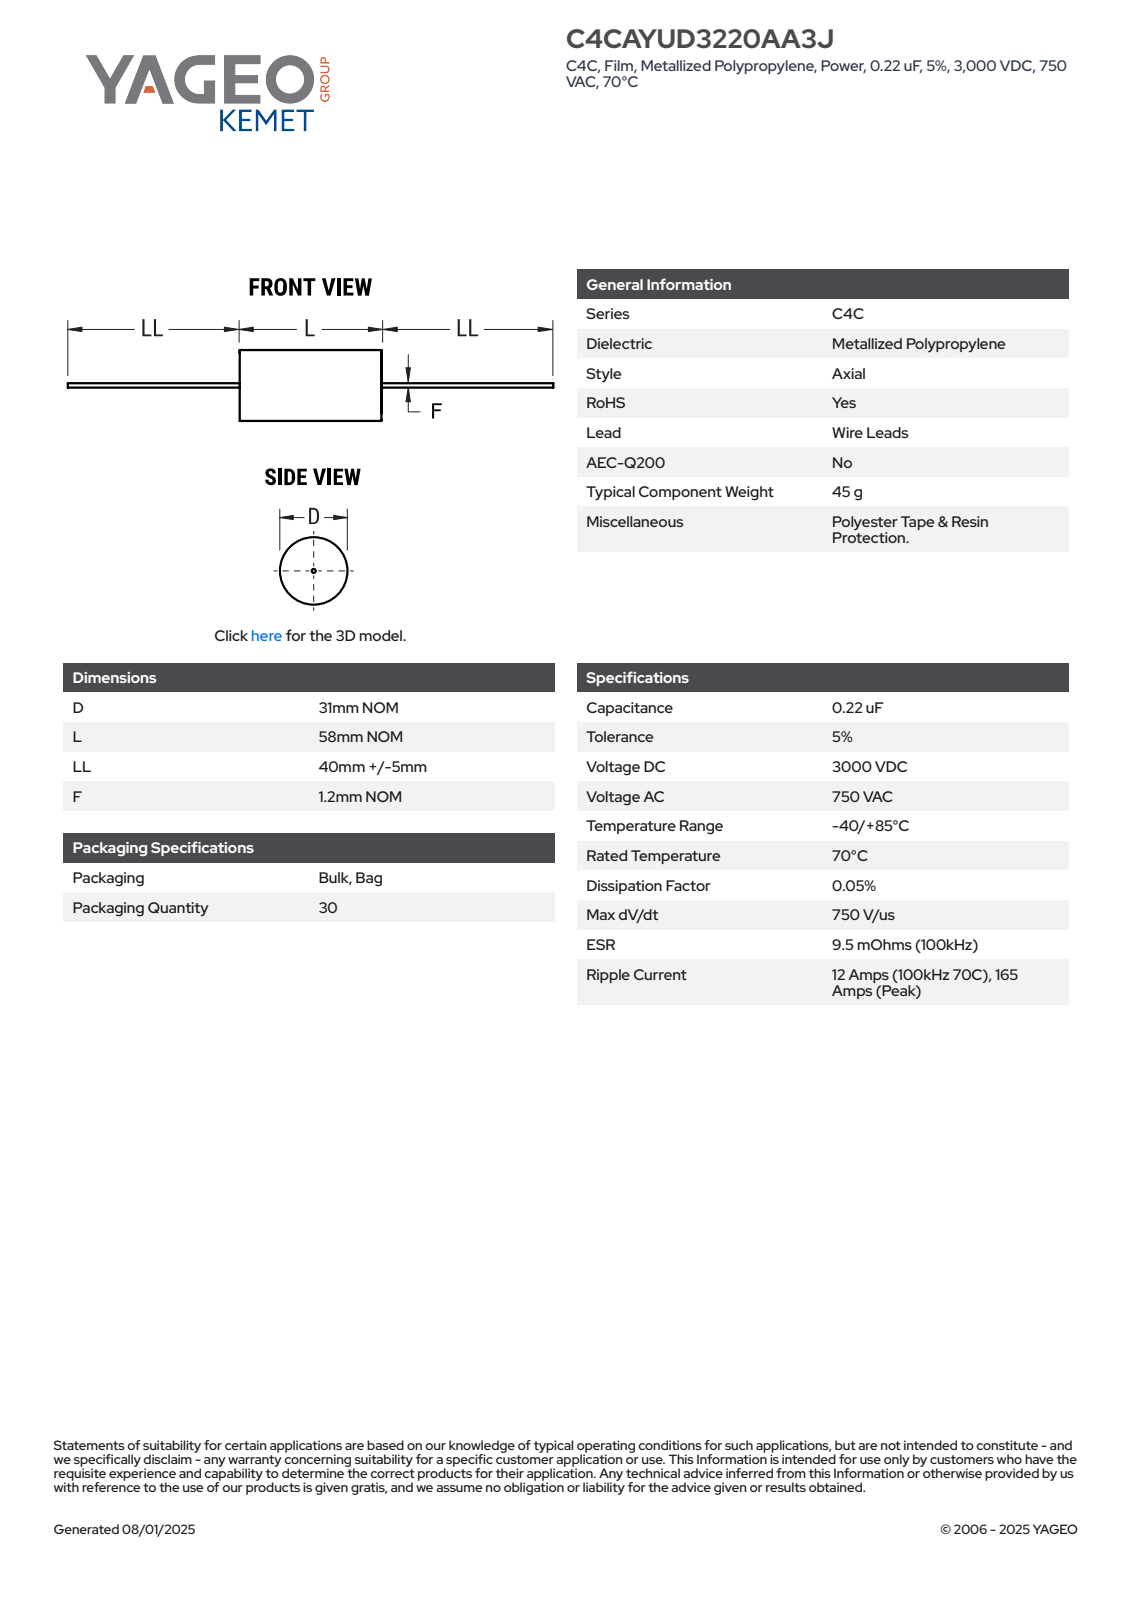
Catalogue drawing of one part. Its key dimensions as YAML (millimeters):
part_name: "CFP_ACWF_31X58_D31L58LL45F1.2"
step_written_by: "SolidWorks 2014 (AUTOMOTIVE_DESIGN)"
units: millimeters
bodies: {solids: 2, faces: 87, planar: 28, cylindrical: 28, other: 31}
overall_size: [148, 31, 31]
volume: 43878
surface_area: 9006
round_bosses_or_shafts:
  - {diameter: 31, count: 1}
  - {diameter: 1.2, count: 1}
partial_cylinders:
  - {radius: 15.49, count: 1}
face_to_face_distances: [58.01, 58, 45, 103, 44.99, 148, 103.01]
